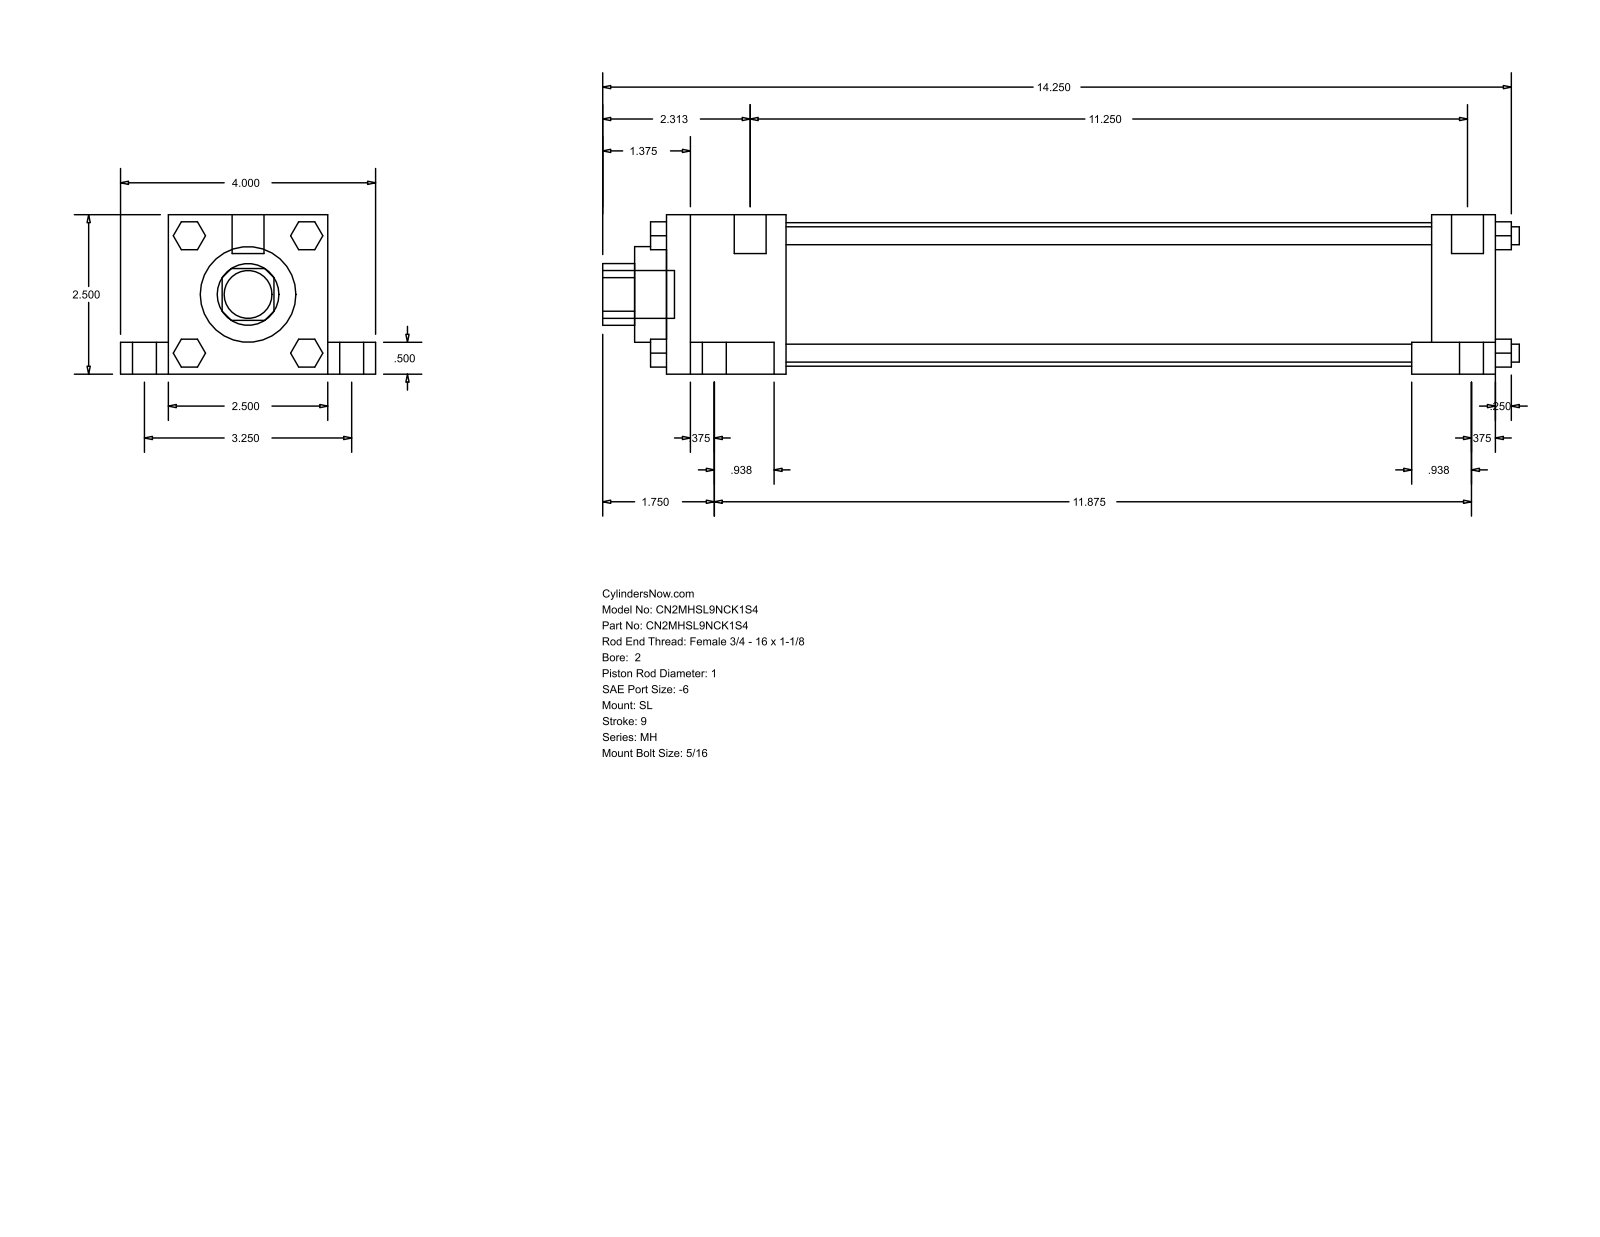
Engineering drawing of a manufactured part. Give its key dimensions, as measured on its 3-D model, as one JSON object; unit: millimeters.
{"part_name": "MH_SL__0200_1", "step_written_by": "GSSL Pune (CONFIG_CONTROL_DESIGN)", "units": "millimeters", "bodies": {"solids": 0, "faces": 148, "planar": 112, "cylindrical": 36, "other": 0}, "overall_size": [365.12, 101.6, 63.5], "round_holes": [[25.4, 1], [38.1, 1], [57.15, 1]], "round_bosses_or_shafts": [[15.88, 4], [9.53, 4], [7.14, 4], [5.56, 4], [12.7, 2], [19.05, 1]], "partial_cylinders_radius": [[12.29, 1]], "face_to_face_distances": [63.5, 330.2, 12.7, 19.05, 50.8, 82.55, 9.52, 25.4, 304.8, 47.63]}
